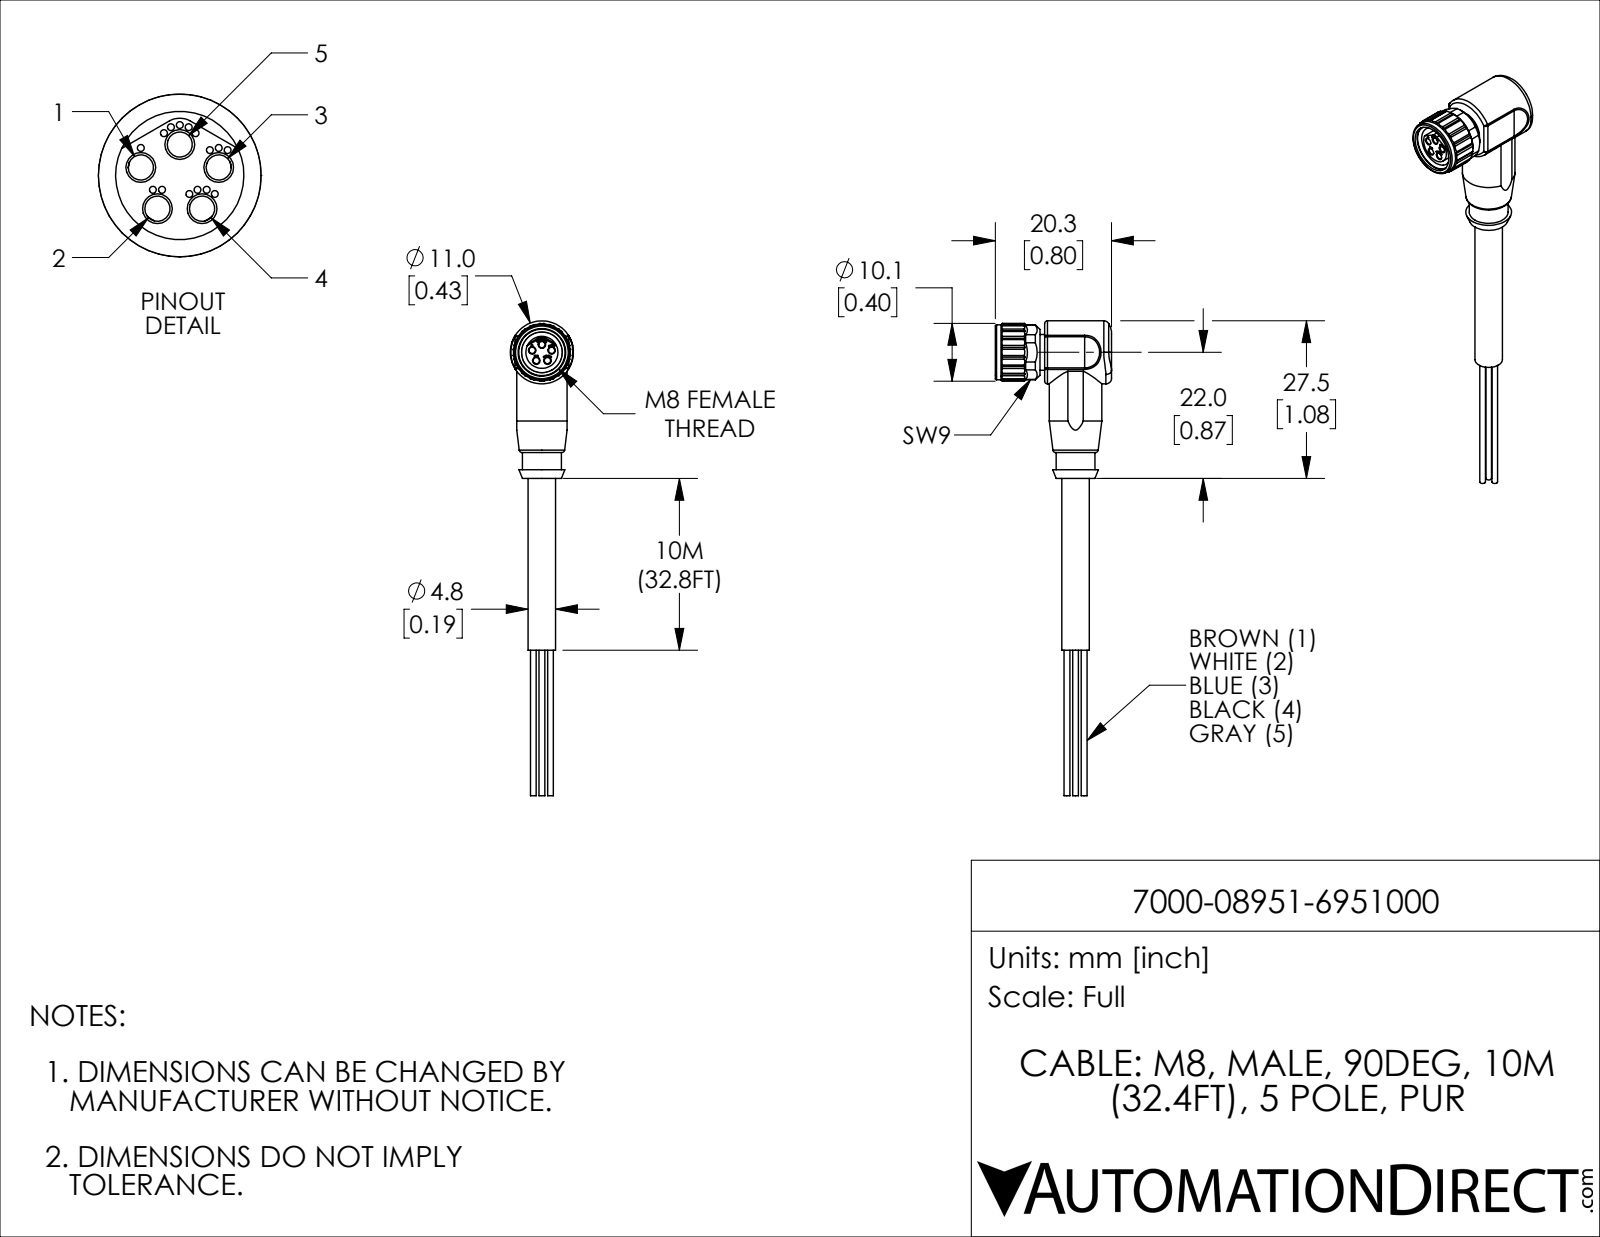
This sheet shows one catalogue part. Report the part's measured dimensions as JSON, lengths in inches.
{"part_name": "7000-08951-6951000", "step_written_by": "SolidWorks 2019 (CONFIG_CONTROL_DESIGN)", "units": "inches", "bodies": {"solids": 1, "faces": 341, "planar": 135, "cylindrical": 152, "other": 54}, "overall_size": [3.264, 0.799, 0.433], "volume_in3": 0.189, "surface_area_in2": 3.917, "round_holes": [[0.012, 15], [0.043, 5], [0.25, 1], [0.28, 1], [0.327, 1]], "round_bosses_or_shafts": [[0.039, 5], [0.433, 1], [0.378, 1], [0.362, 1], [0.268, 1], [0.246, 1], [0.22, 1], [0.189, 1]], "partial_cylinders_radius": [[0.079, 18], [0.02, 8], [0.03, 6], [0.033, 4], [0.008, 2], [0.138, 2], [0.197, 2], [0.022, 1]], "face_to_face_distances": [0.358, 0.461, 0.37, 0.346, 0.357, 0.031, 0.492, 0.354, 0.77, 0.309], "hole_center_spacings": [0.033, 0.016, 0.078, 0.031, 0.044, 0.069, 0.076, 0.099]}
